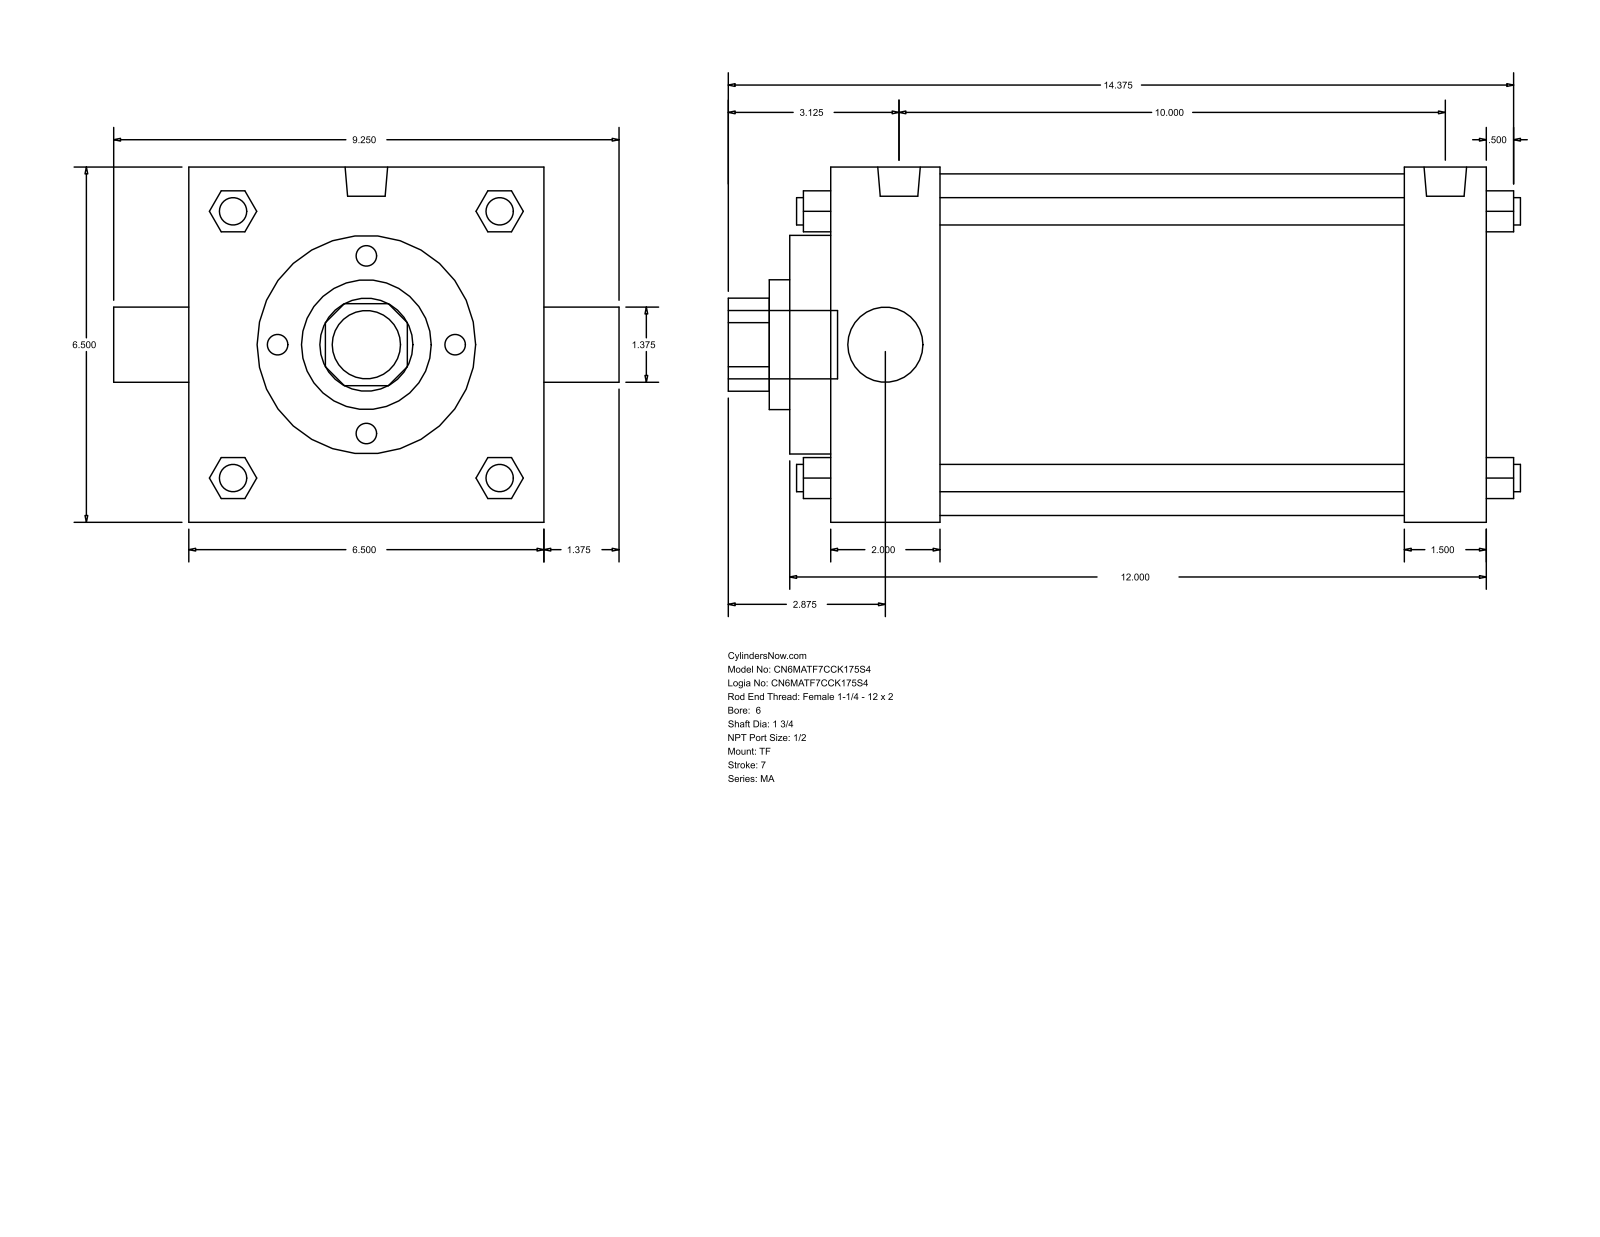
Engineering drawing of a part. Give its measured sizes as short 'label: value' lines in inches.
name: MA_TF__0600_1.75
written by: GSSL Pune (CONFIG_CONTROL_DESIGN)
unit: in
bodies: 0 solids, 122 faces (93 planar, 29 cylindrical, 0 other)
size: 14.5 × 9.25 × 6.5
holes: 1× ⌀1.375, 1× ⌀1.75, 1× ⌀2.375, 1× ⌀4, 1× ⌀6.25
bosses: 4× ⌀0.5, 3× ⌀0.687, 2× ⌀0.778, 1× ⌀1.25
rounds: 1× R0.852
face distances: 6.5, 12, 0.75, 2, 10.5, 10, 8.5, 1.5, 2.75, 11.25
